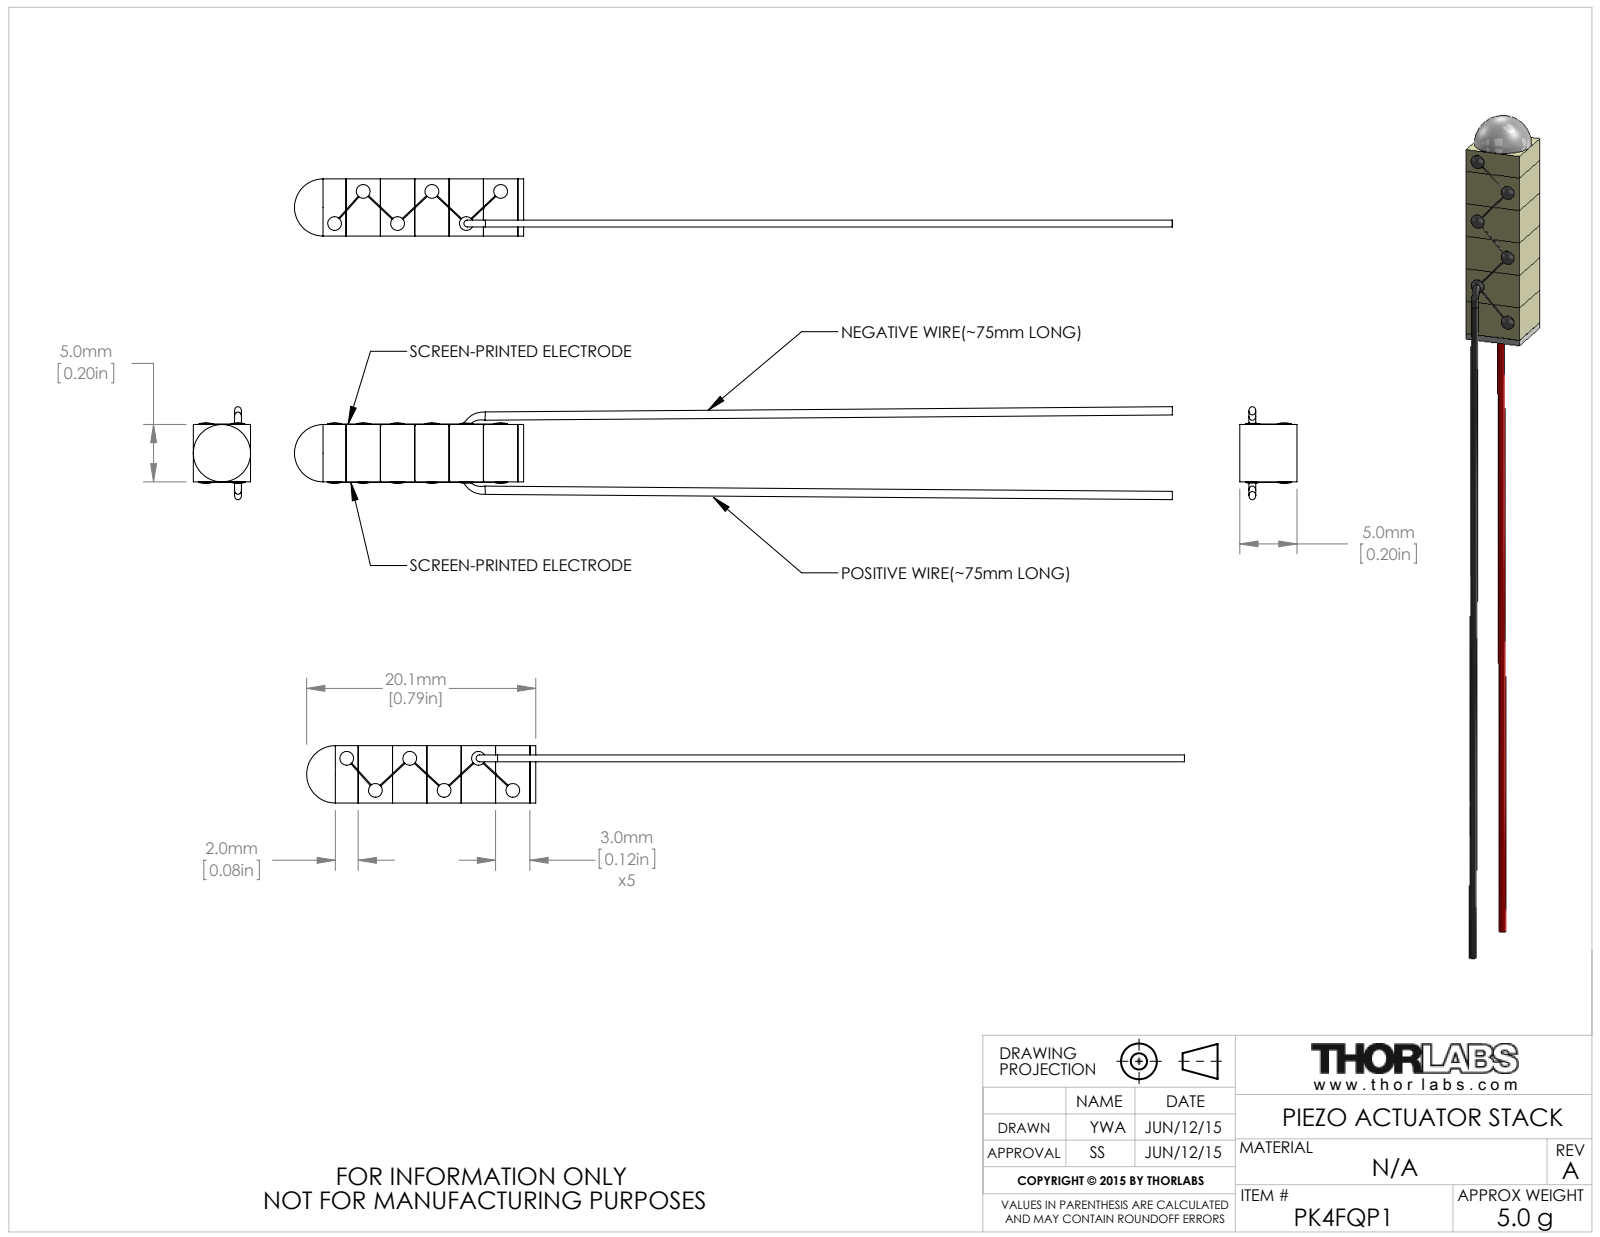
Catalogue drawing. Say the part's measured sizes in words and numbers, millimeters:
The part is named "CTN002966". Its 3-D file was written by "SolidWorks 2014 (AUTOMOTIVE_DESIGN)". It is 13 solids with 145 faces: 67 planar, 44 cylindrical and 34 other. Overall it measures 76.65 by 8.12 by 5 millimeters. Its volume is 514 cubic millimeters and its surface area 1 014 square millimeters. Round bosses or shafts: 6 of diameter 1.2. The main face-to-face distances are 3, 5, 6, 9, 12, 0.5, 3.51, 6.51, 9.51, 12.51.
